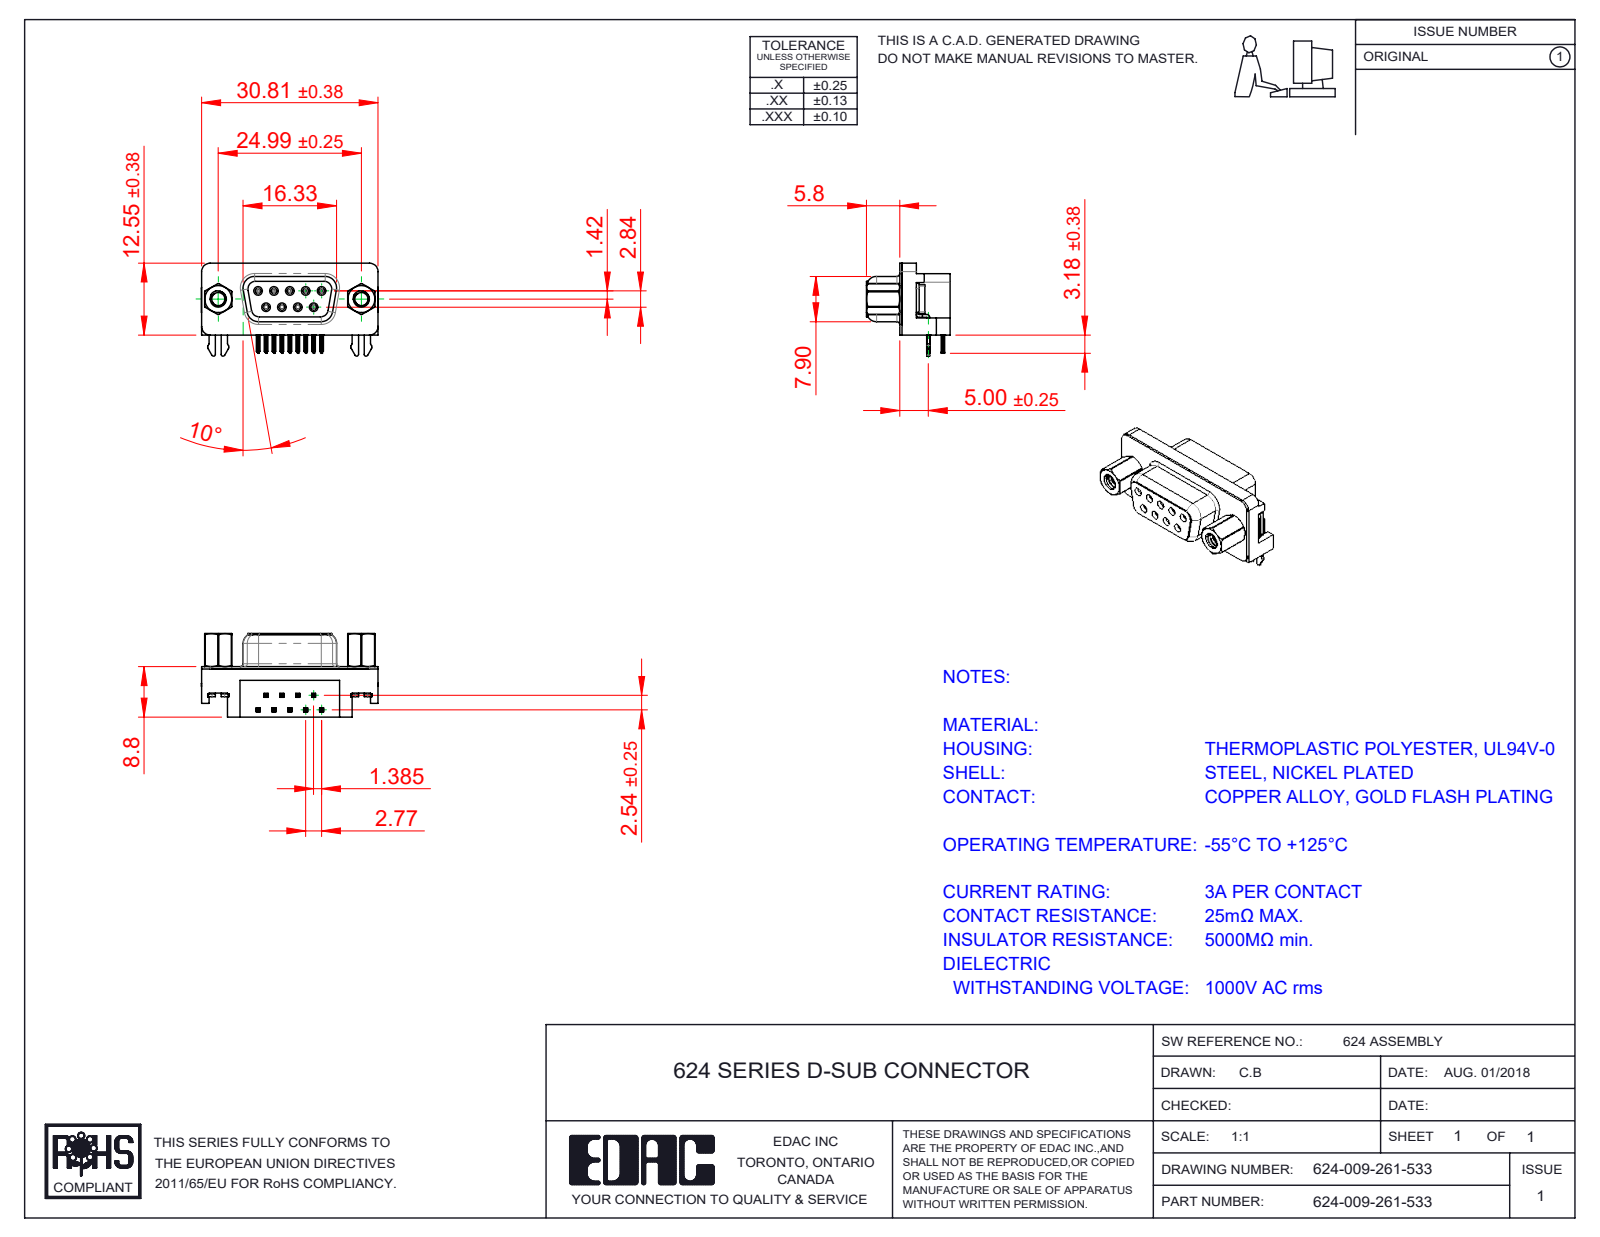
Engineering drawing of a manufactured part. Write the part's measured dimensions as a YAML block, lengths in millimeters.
part_name: "624 Shell_9 Socket; 624 Housing_9 Socket; 624-009-261-533; 624 4-40 Hex Standoff 5 (+4 more)"
step_written_by: "SolidWorks 2016 (CONFIG_CONTROL_DESIGN)"
units: millimeters
bodies: {solids: 17, faces: 1676, planar: 692, cylindrical: 478, other: 506}
overall_size: [30.89, 16.25, 14.6]
volume: 3155
surface_area: 4867
round_holes:
  - {diameter: 0.8, count: 9}
  - {diameter: 0.9, count: 9}
  - {diameter: 2.26, count: 2}
  - {diameter: 2.29, count: 2}
  - {diameter: 4, count: 2}
  - {diameter: 4.8, count: 2}
  - {diameter: 5, count: 2}
round_bosses_or_shafts:
  - {diameter: 1.2, count: 9}
  - {diameter: 4.9, count: 2}
  - {diameter: 4.75, count: 2}
  - {diameter: 3.9, count: 2}
  - {diameter: 2.79, count: 2}
partial_cylinders:
  - {radius: 0.1, count: 72}
  - {radius: 0.15, count: 36}
  - {radius: 0.35, count: 18}
  - {radius: 0.5, count: 10}
  - {radius: 1, count: 10}
  - {radius: 0.34, count: 9}
  - {radius: 0.25, count: 8}
  - {radius: 1.35, count: 8}
face_to_face_distances: [0.4, 8.4, 8.8, 2.9, 6.2, 2.5, 5.9, 0.35, 0.85, 10.69]
hole_center_spacings: [3.16, 2.77, 5.54, 5.03, 5.04, 8.31, 7.48, 7.49]
